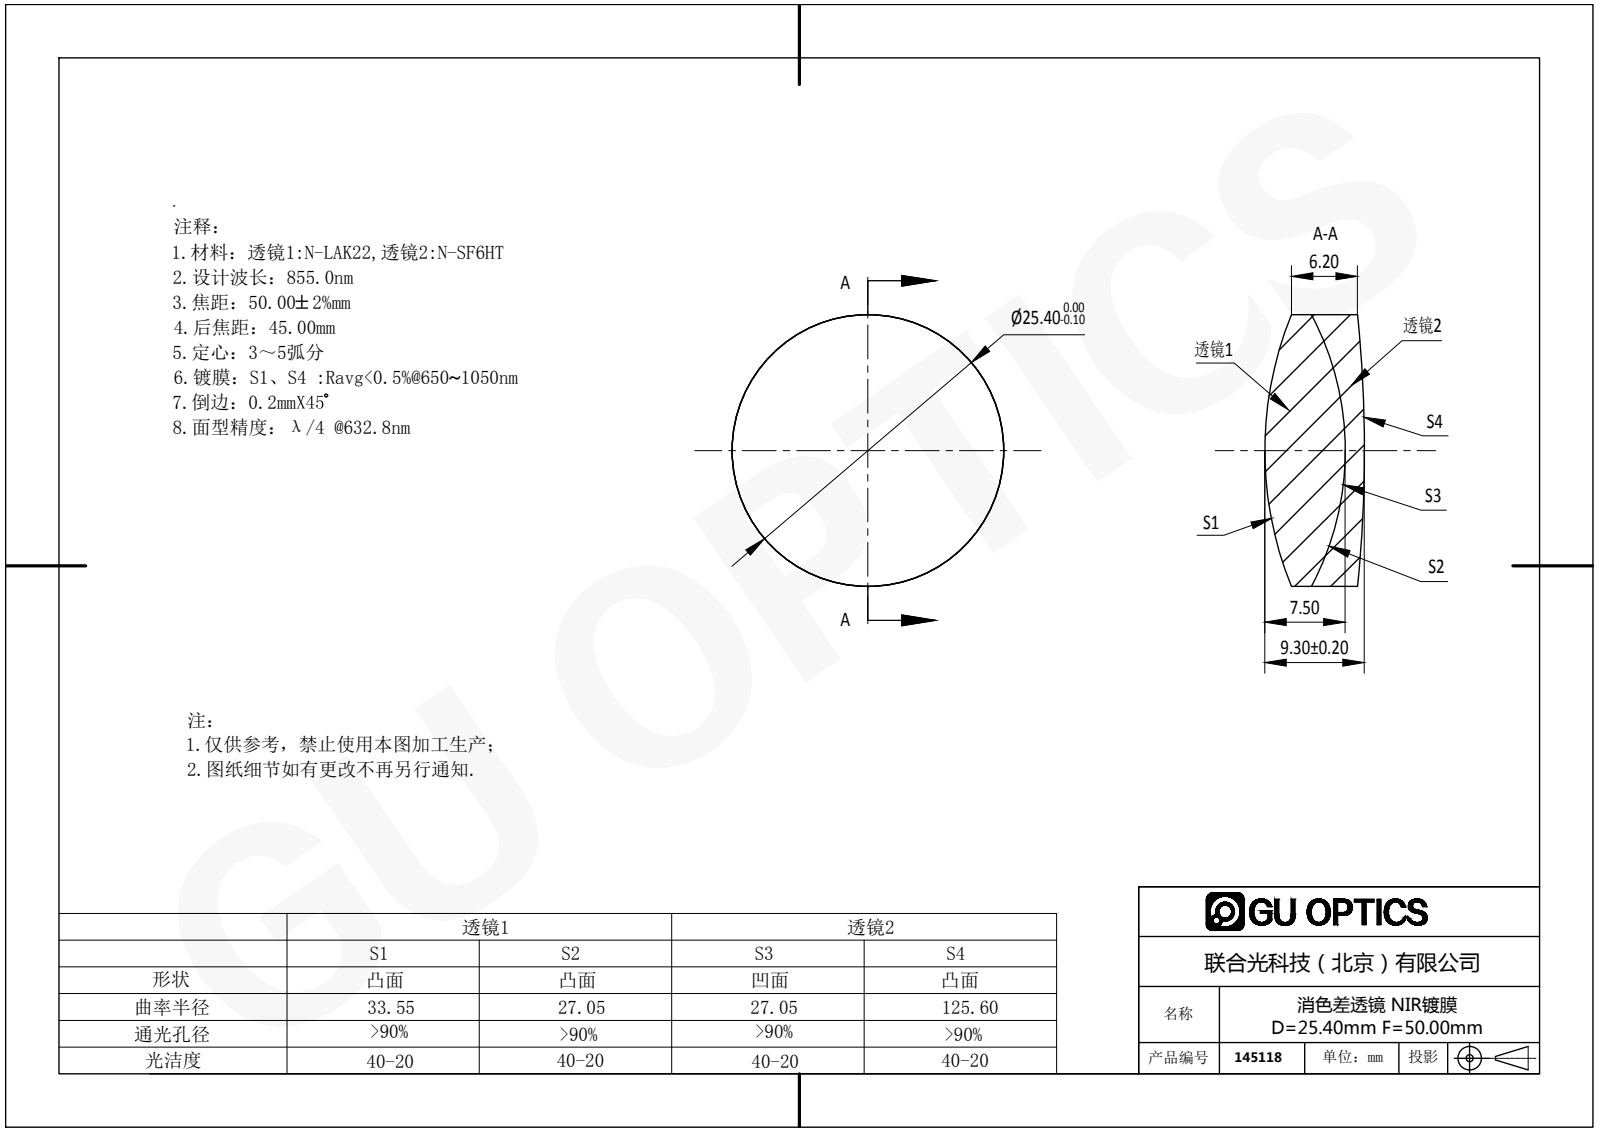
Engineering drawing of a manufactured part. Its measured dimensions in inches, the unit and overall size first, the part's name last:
Units: inches
Overall size (bounding box): 1 × 1 × 0.366
Round bosses / shafts (diameter × count): ⌀1 ×1
Volume: 0.24 in³ · Surface area: 4.033 in²
Bodies: 2 solids, 12 faces (0 planar, 4 cylindrical, 8 other)
Part name (STEP PRODUCT): 145118
STEP written by: SolidWorks 2016 (AUTOMOTIVE_DESIGN)
